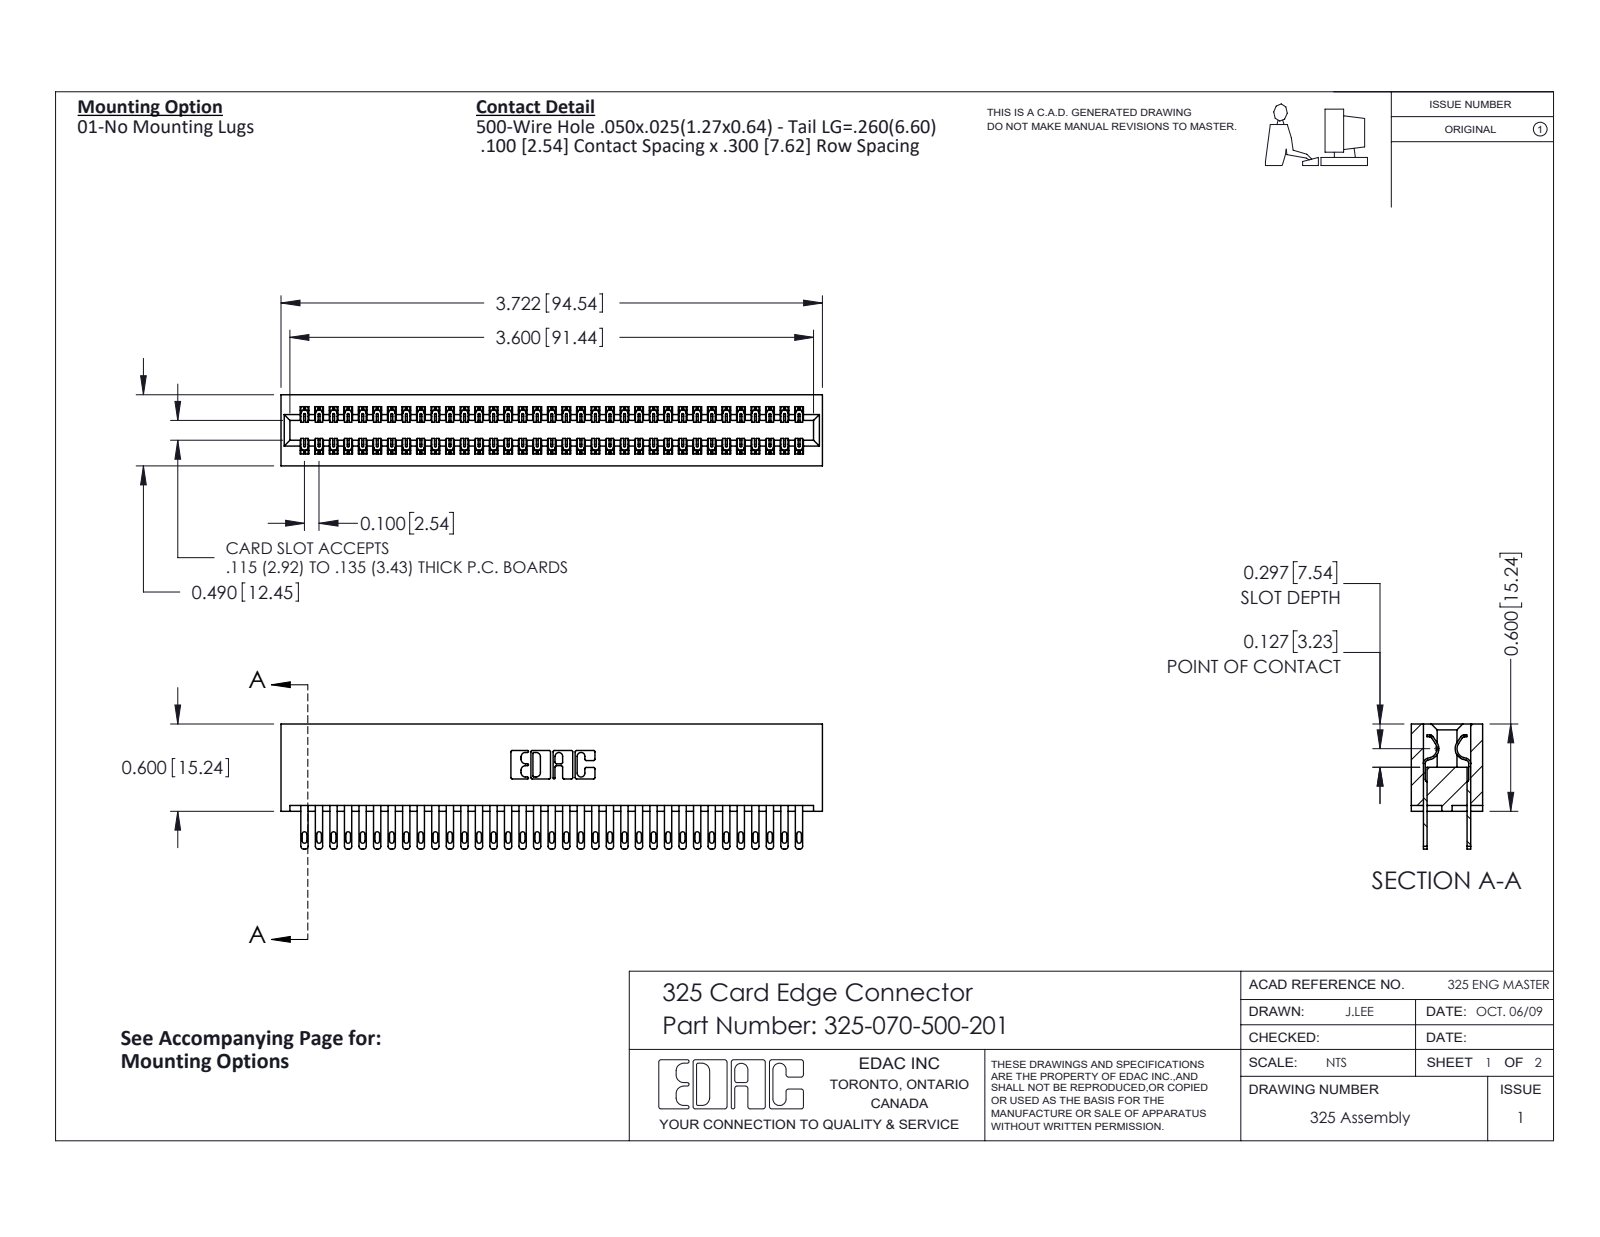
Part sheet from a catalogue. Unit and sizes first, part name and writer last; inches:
Units: inches
Overall size (bounding box): 3.722 × 0.86 × 0.49
Partial cylindrical surfaces — rounded edges, fillets, slot ends (radius × count): R0.006 ×105, R0.016 ×70, R0.02 ×70, R0.01 ×22, R0.007 ×6, R0.031 ×6, R0.026 ×3, R0.014 ×2
Main face-to-face distances: 0.083, 0.407, 0.3, 0.107, 0.383, 0.025, 0.325, 0.49, 0.275, 0.56
Volume: 0.791 in³ · Surface area: 26.22 in²
Bodies: 71 solids, 3466 faces (2166 planar, 1300 cylindrical, 0 other)
Part name (STEP PRODUCT): 325-292-001_325-293-100; 325-070-500-201; 325 Part_Lugless
STEP written by: SolidWorks 2016 (CONFIG_CONTROL_DESIGN)
